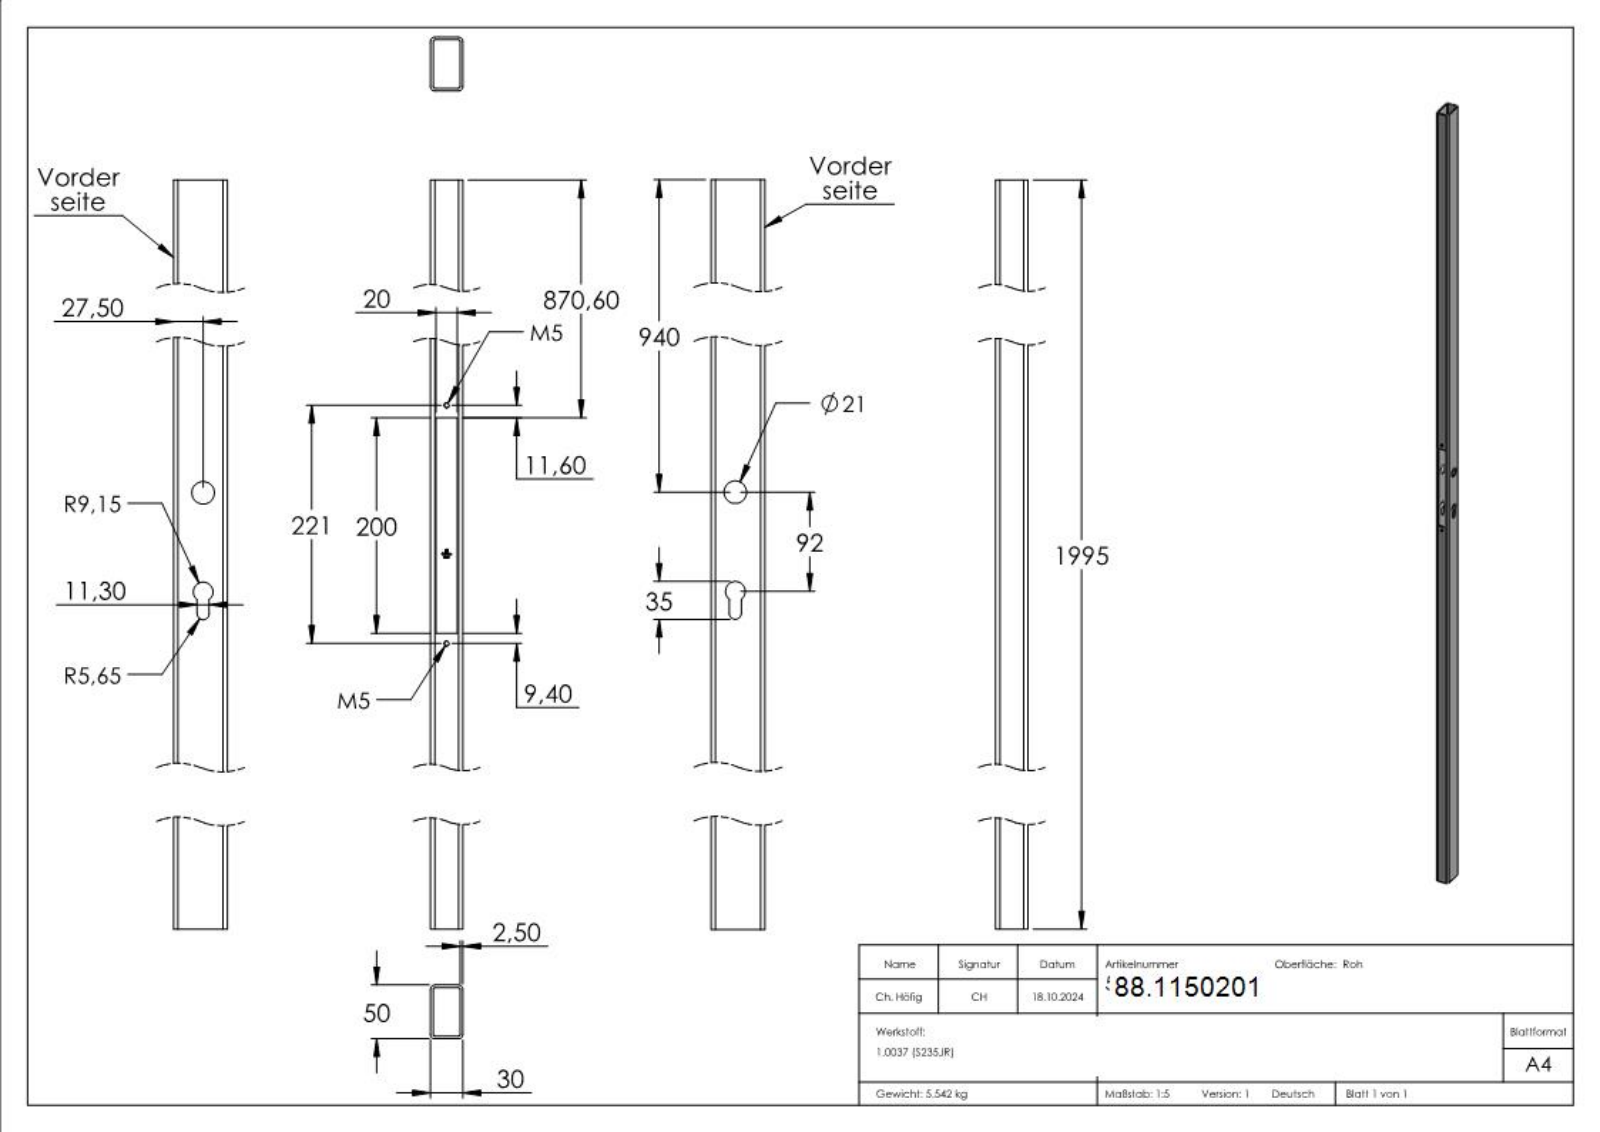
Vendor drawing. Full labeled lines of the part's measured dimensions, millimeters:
Part name (STEP PRODUCT): 50201
STEP written by: SolidWorks 2018 (CONFIG_CONTROL_DESIGN)
Units: millimetres
Bodies: 1 solid, 247 faces (131 planar, 16 cylindrical, 100 other)
Overall size (bounding box): 1995 × 50 × 30
Volume: 710 551 mm³ · Surface area: 571 119 mm²
Round holes (diameter × count): ⌀4.2 ×2, ⌀21 ×1
Partial cylindrical surfaces — rounded edges, fillets, slot ends (radius × count): R1.5 ×4, R4 ×4, R5.65 ×1, R9.15 ×1
Main face-to-face distances: 2.5, 27.5, 25, 30, 47.5, 50, 45, 5, 22.5, 20
Hole centre spacings: 221
